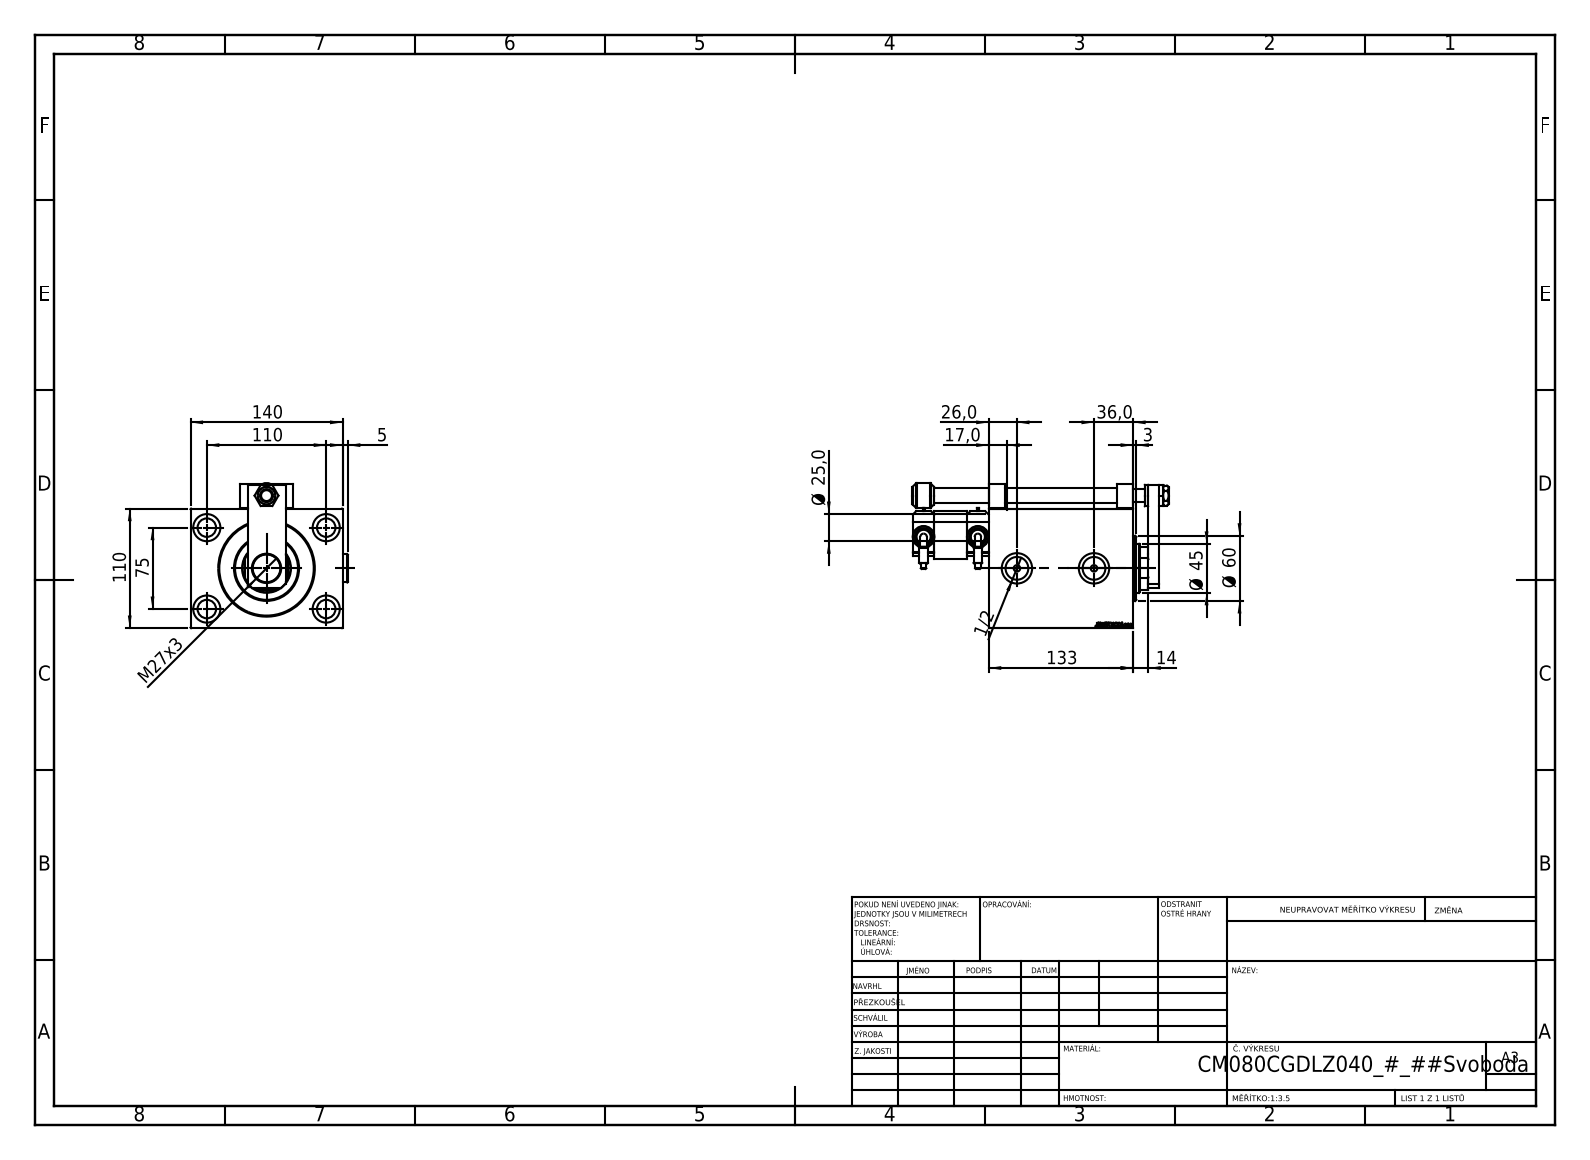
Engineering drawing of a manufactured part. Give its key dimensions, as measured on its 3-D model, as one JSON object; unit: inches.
{"part_name": "ZARAZKA_P; SWITCH_P_FRONT_BACK; SWITCH DIM W_B; MIDDLE (+8 more)", "step_written_by": "SolidWorks 2019 (CONFIG_CONTROL_DESIGN)", "units": "inches", "bodies": {"solids": 16, "faces": 1169, "planar": 558, "cylindrical": 142, "other": 469}, "overall_size": [9.291, 5.705, 5.256], "volume_in3": 119.3, "surface_area_in2": 421.7, "round_holes": [[0.157, 4], [0.315, 4], [0.669, 4], [0.984, 4], [0.236, 2], [0.825, 2], [1.102, 2], [0.472, 1], [0.512, 1], [0.551, 1], [1.004, 1], [1.063, 1]], "round_bosses_or_shafts": [[0.787, 3], [1.024, 2], [0.63, 2], [0.551, 2], [0.315, 2], [0.236, 2], [0.198, 2], [2.362, 1]], "partial_cylinders_radius": [[0.118, 1], [0.866, 1]], "face_to_face_distances": [4.331, 5.512, 5.236, 0.827, 4.409, 1.969, 0.551, 0.787, 1.575, 1.614], "hole_center_spacings": [2.621, 0.787, 2.457, 2.953, 4.331, 4.646, 4.649, 4.712]}
